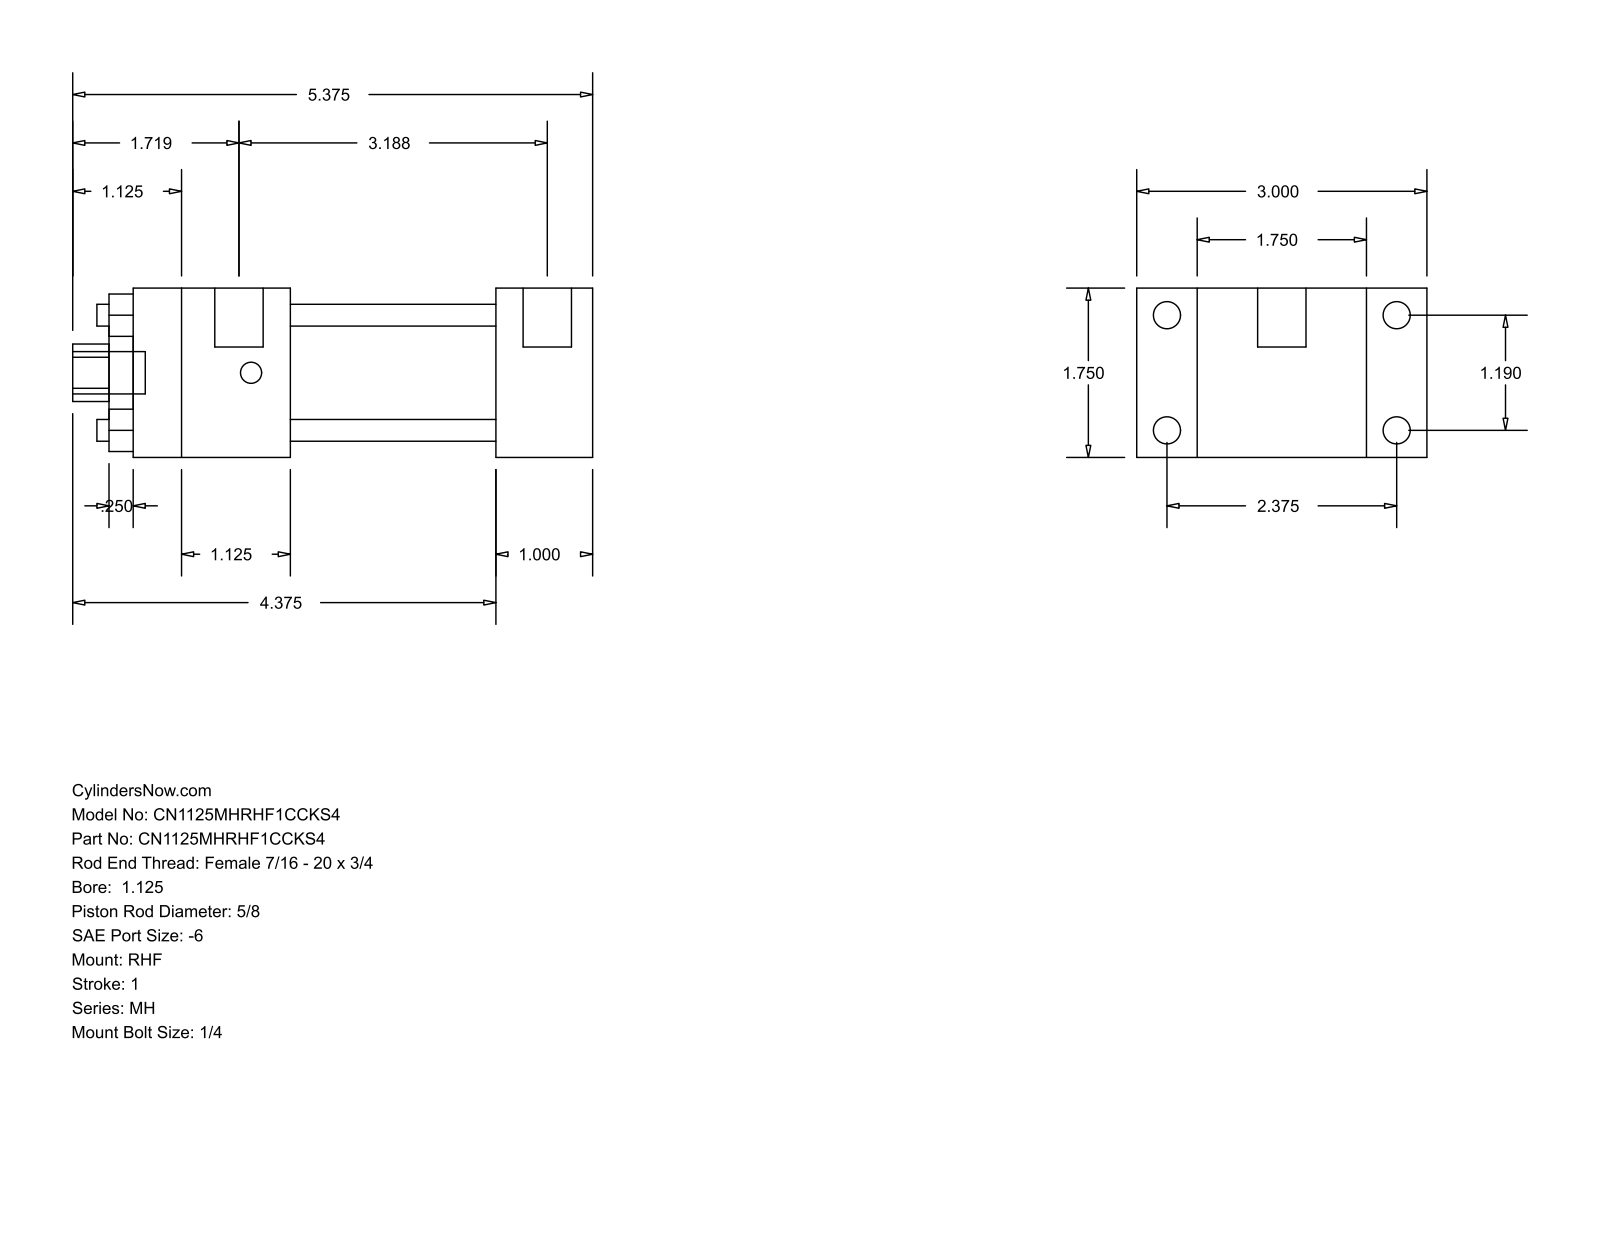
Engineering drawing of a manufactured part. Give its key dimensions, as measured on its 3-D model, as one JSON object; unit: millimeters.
{"part_name": "MH_RHF__0112_0.625", "step_written_by": "GSSL Pune (CONFIG_CONTROL_DESIGN)", "units": "millimeters", "bodies": {"solids": 0, "faces": 88, "planar": 60, "cylindrical": 28, "other": 0}, "overall_size": [136.53, 76.2, 44.45], "round_holes": [[5.71, 4], [15.88, 1], [28.57, 1], [34.92, 1]], "round_bosses_or_shafts": [[7.14, 4], [5.56, 4], [12.7, 2], [11.11, 1]], "partial_cylinders_radius": [[7.54, 1]], "face_to_face_distances": [44.46, 15.87, 60.33, 25.41, 76.2, 53.97, 79.38, 41.27, 95.24, 120.65], "hole_center_spacings": [21.37, 30.22, 42.74]}
